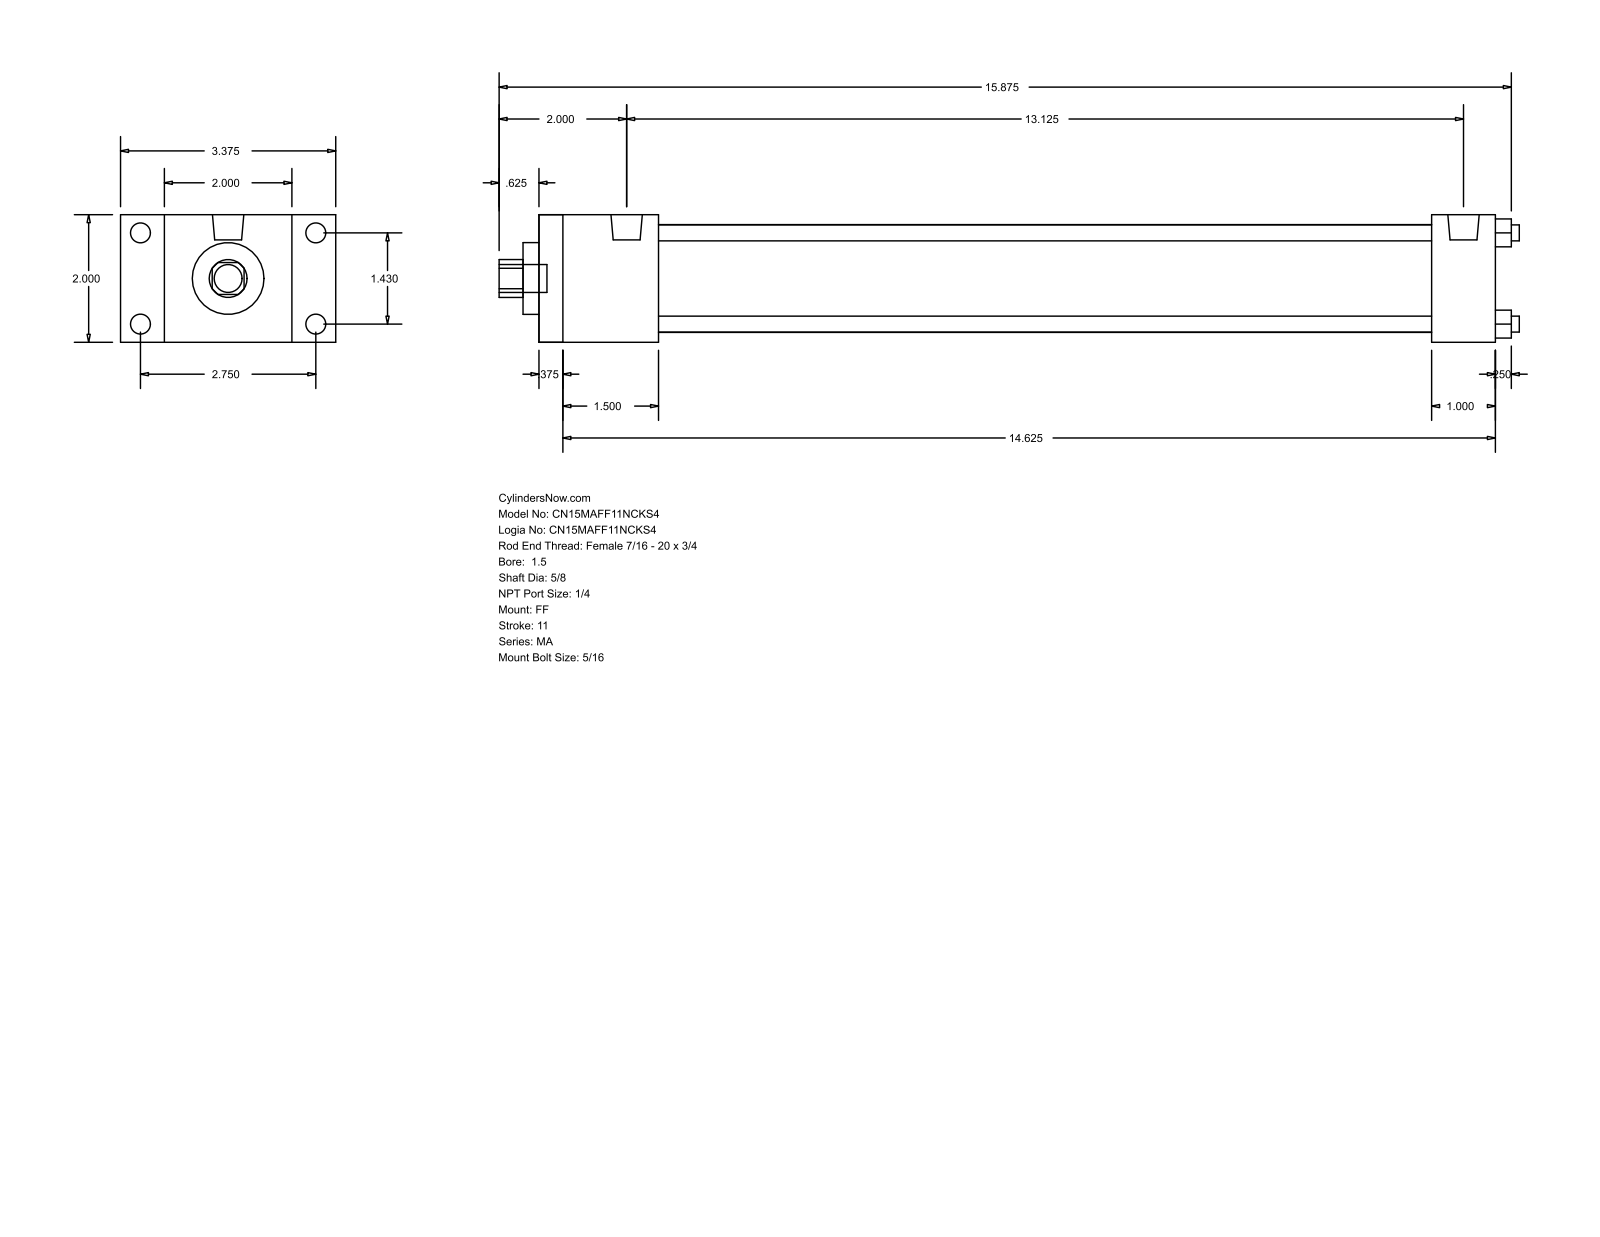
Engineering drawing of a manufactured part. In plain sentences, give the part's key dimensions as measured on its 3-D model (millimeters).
The part is named "MA_FF__0150_0.625". Its 3-D file was written by "GSSL Pune (CONFIG_CONTROL_DESIGN)". It is 0 solids with 92 faces: 64 planar, 28 cylindrical and 0 other. Overall it measures 406.4 by 85.72 by 50.8 millimeters. Round holes: 4 of diameter 6.35, 1 of diameter 15.88, 1 of diameter 28.57, 1 of diameter 42.93. Round bosses or shafts: 8 of diameter 7.94, 2 of diameter 12.49, 1 of diameter 11.11. Partial cylindrical surfaces (rounded edges, fillets, slot ends): 1 of radius 7.54. The main face-to-face distances are 50.8, 381, 9.52, 371.48, 25.4, 47.62, 355.6, 38.1, 346.08, 307.98. The hole center spacings are 25.68, 36.32, 51.36.
